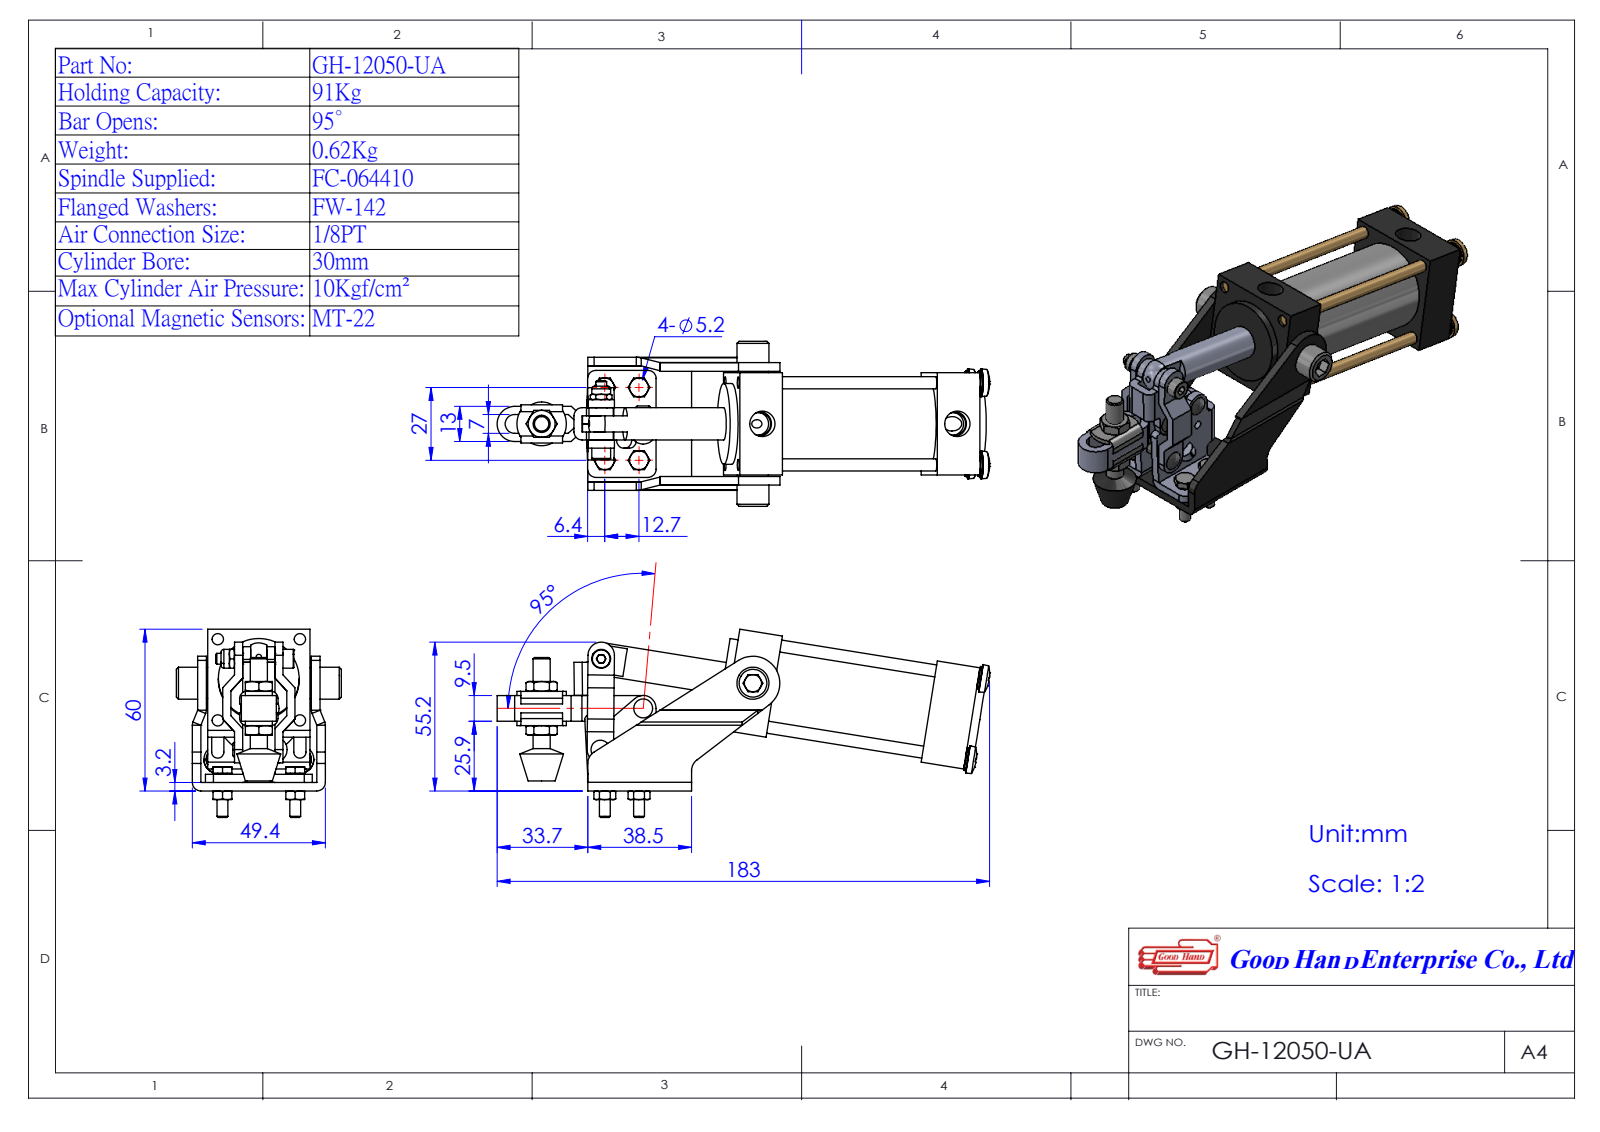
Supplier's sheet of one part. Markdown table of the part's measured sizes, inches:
| quantity | value |
| --- | --- |
| part name | 12050A-CYLINDER-1^GH-12050-UA(簡化)-1; Group1^GH-12050-UA(簡化)-1; Group4^GH-12050-UA(簡化)-1; Group7^GH-12050-UA(簡化)-1 (+4 more) |
| STEP written by | SolidWorks 2016 (AUTOMOTIVE_DESIGN) |
| units | inches |
| bodies | 8 solids, 847 faces (398 planar, 221 cylindrical, 228 other) |
| overall size | 7.2 × 2.749 × 2.412 |
| volume | 7.9 in³ |
| surface area | 96.7 in² |
| round holes (diameter × count) | 0.118 × 4, 0.236 × 2, 0.311 × 2, 0.472 × 2, 0.197 × 1, 0.248 × 1, 1.181 × 1 |
| round bosses / shafts (diameter × count) | 0.276 × 5, 0.157 × 5, 0.406 × 4, 0.177 × 4, 1.181 × 3, 1.378 × 1, 0.472 × 1, 0.469 × 1 |
| partial cylindrical surfaces (radius × count) | 0.118 × 10, 0.039 × 6, 0.126 × 6, 0.102 × 4, 0.197 × 3, 0.079 × 2, 0.177 × 2, 0.193 × 2 |
| main face-to-face distances | 0.118, 0.126, 0.512, 0.63, 0.984, 0.236, 0.354, 0.866, 0.098, 0.61 |
| hole center spacings | 0.603, 0.606, 0.724, 0.869, 0.95, 1.327, 1.646, 2.24 |
